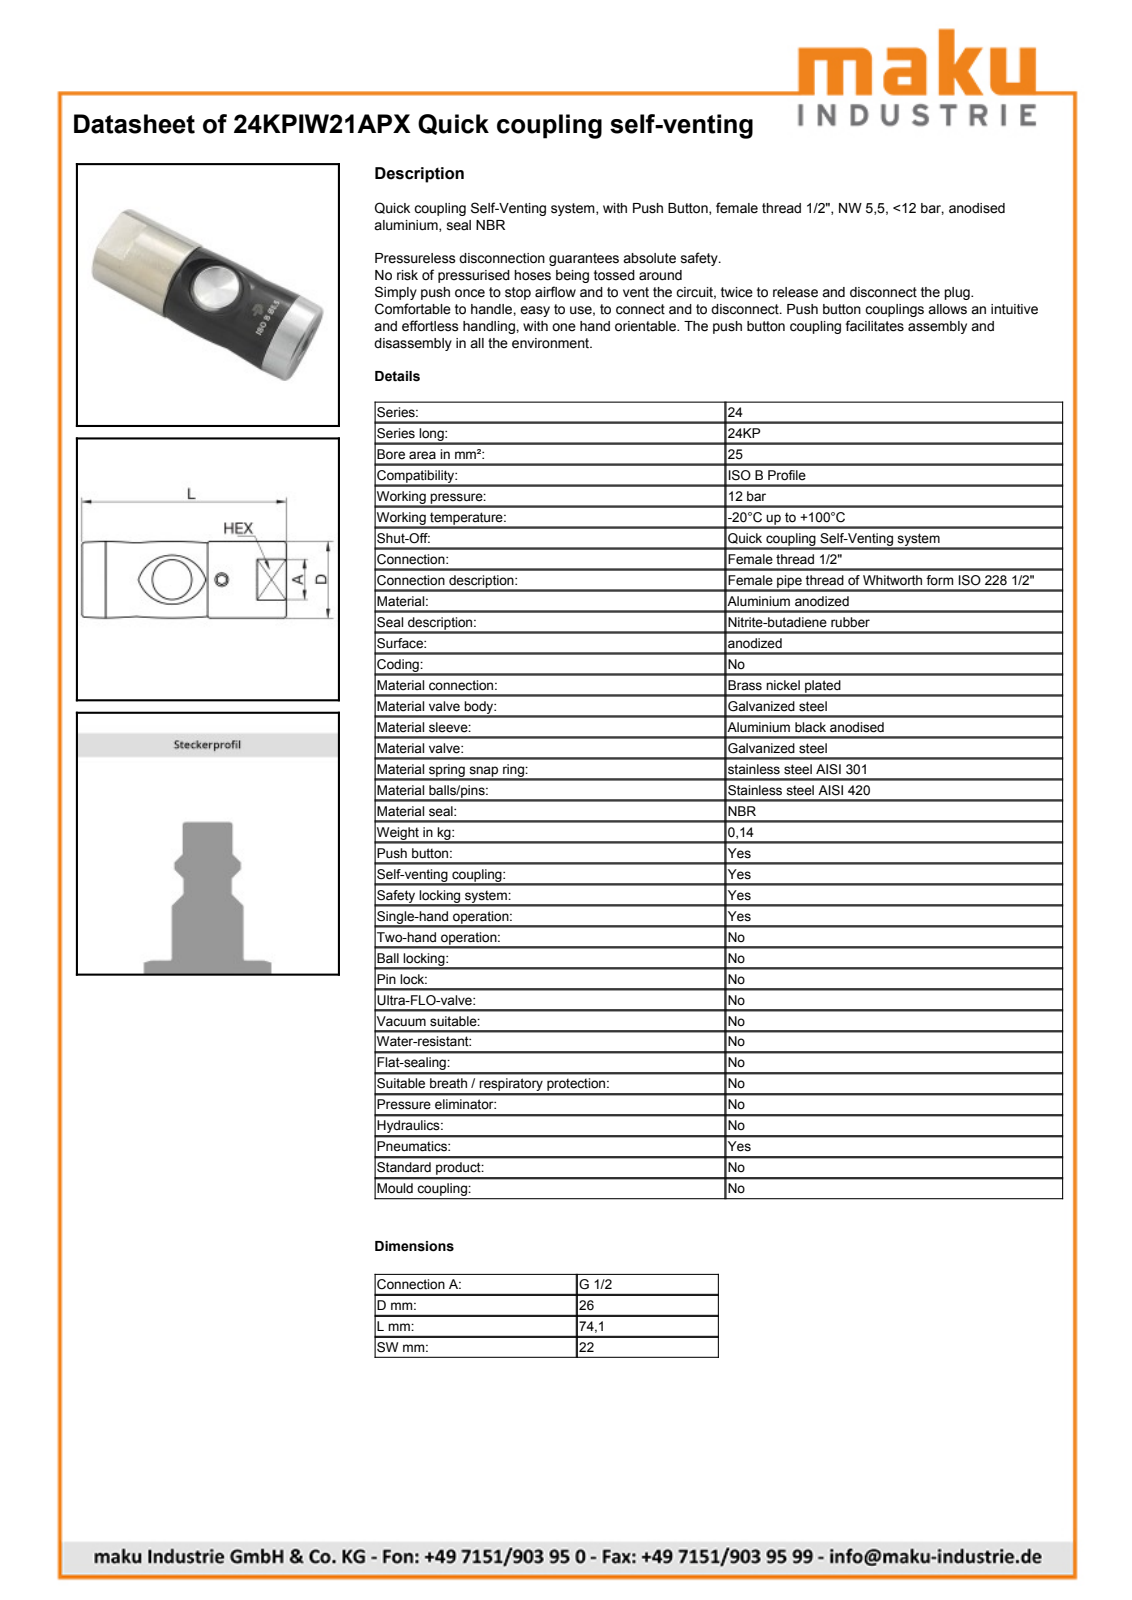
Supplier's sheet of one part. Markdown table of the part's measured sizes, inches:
| quantity | value |
| --- | --- |
| part name | 24KPIW21APX |
| STEP written by | Autodesk Inventor 2019 (CONFIG_CONTROL_DESIGN) |
| units | inches |
| bodies | 39 solids, 221 faces (62 planar, 72 cylindrical, 87 other) |
| overall size | 2.917 × 1.024 × 1.024 |
| volume | 2.378 in³ |
| surface area | 38.84 in² |
| round holes (diameter × count) | 0.488 × 2, 0.138 × 1, 0.256 × 1, 0.378 × 1, 0.38 × 1, 0.417 × 1, 0.433 × 1, 0.472 × 1, 0.482 × 1, 0.535 × 1, 0.591 × 1, 0.626 × 1 |
| round bosses / shafts (diameter × count) | 1.024 × 1, 0.886 × 1, 0.866 × 1, 0.807 × 1, 0.713 × 1, 0.653 × 1, 0.65 × 1, 0.622 × 1 |
| partial cylindrical surfaces (radius × count) | 0.244 × 2 |
| main face-to-face distances | 1.697, 1.378, 0.319, 0.039, 0.629, 2.007, 2.326, 0.63, 2.008, 2.327 |
| hole center spacings | 0.024, 0.028, 0.051, 0.671 |
